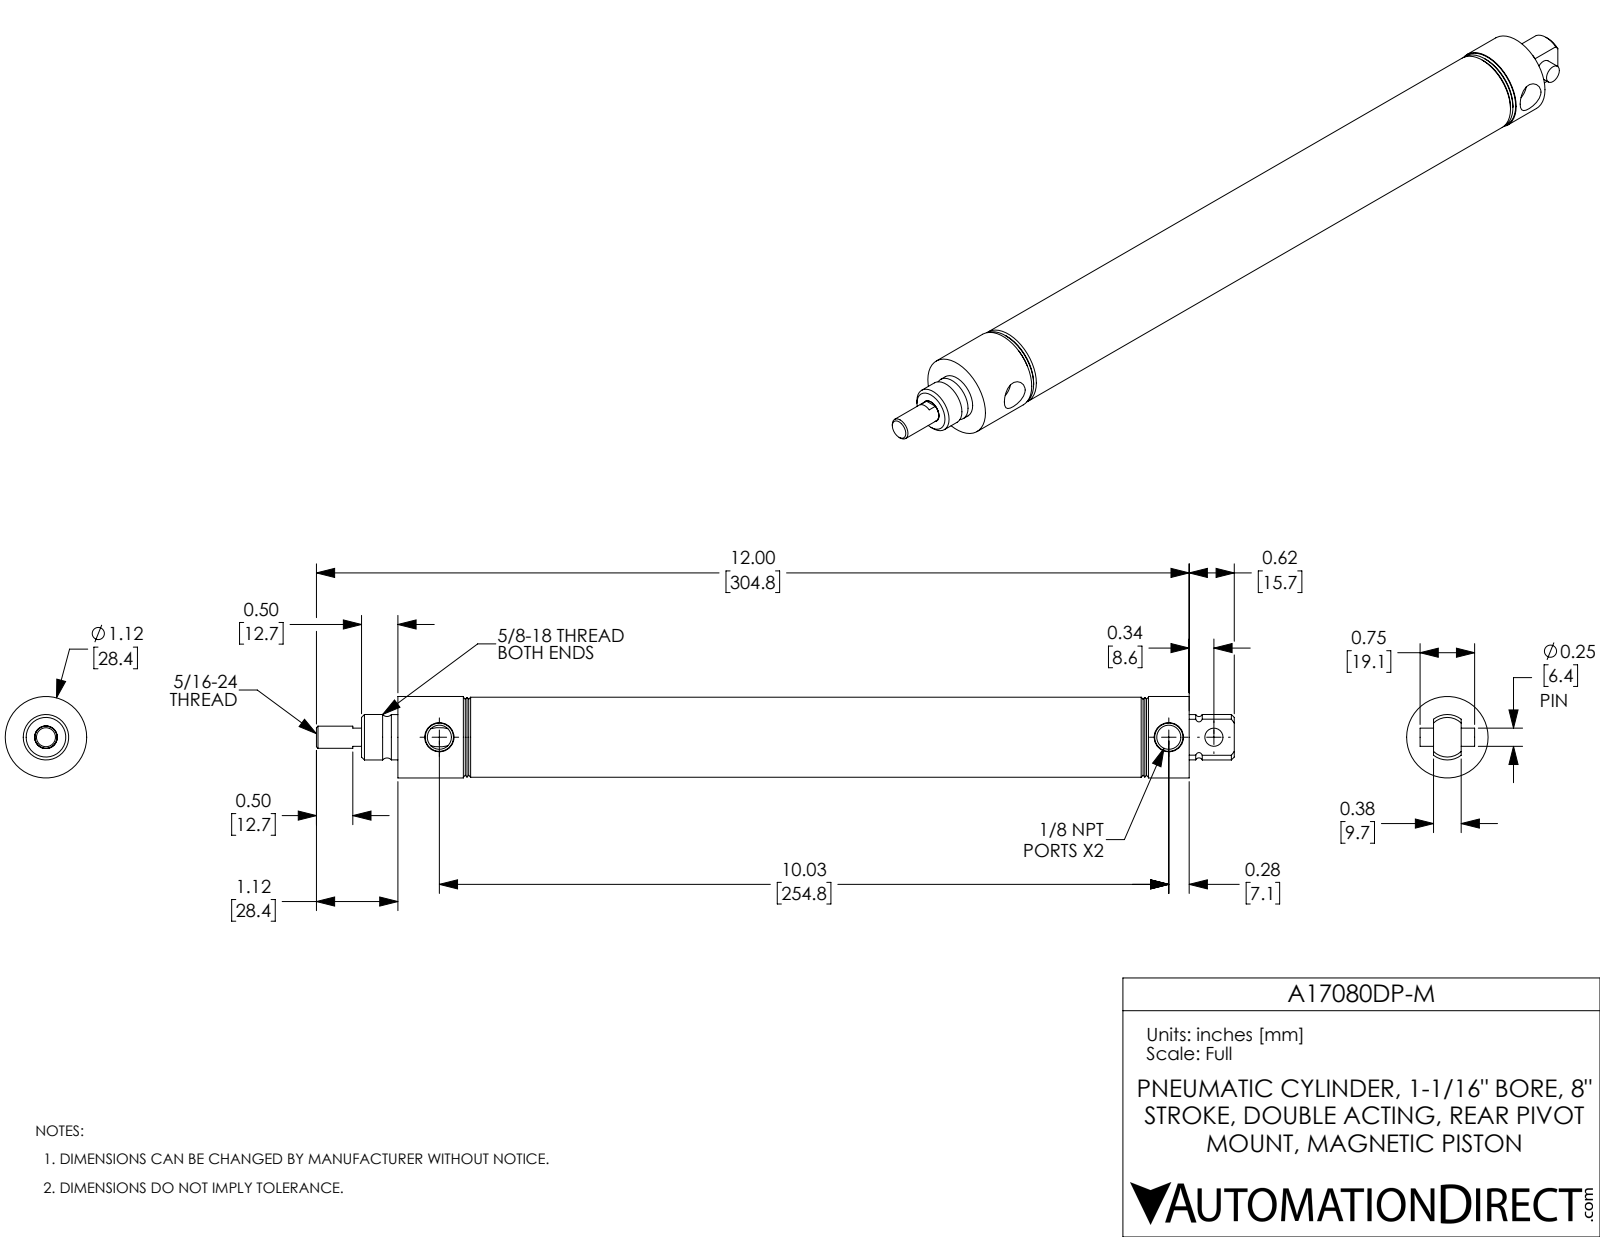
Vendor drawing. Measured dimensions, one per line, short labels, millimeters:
name: A17080DP-M; A17080DP-M-PIN; A17080DP-M-Rod; A17080DP-M-MainBody
written by: SolidWorks 2017 (AUTOMOTIVE_DESIGN)
unit: mm
bodies: 3 solids, 92 faces (22 planar, 32 cylindrical, 38 other)
size: 320.5 × 28.4 × 28.4
volume: 67 960 mm³; area: 57 390 mm²
holes: 2× ⌀8.4, 1× ⌀6.4, 1× ⌀7.9, 1× ⌀27
bosses: 1× ⌀28.4, 1× ⌀27.9, 1× ⌀15.9, 1× ⌀15.8, 1× ⌀7.7
rounds: 1× R8
face distances: 12.7, 246.1, 215.9, 203.2, 30.2, 42.9, 246.1, 276.4, 233.4, 30.2
hole spacings: 15.7, 254.8, 270.5
